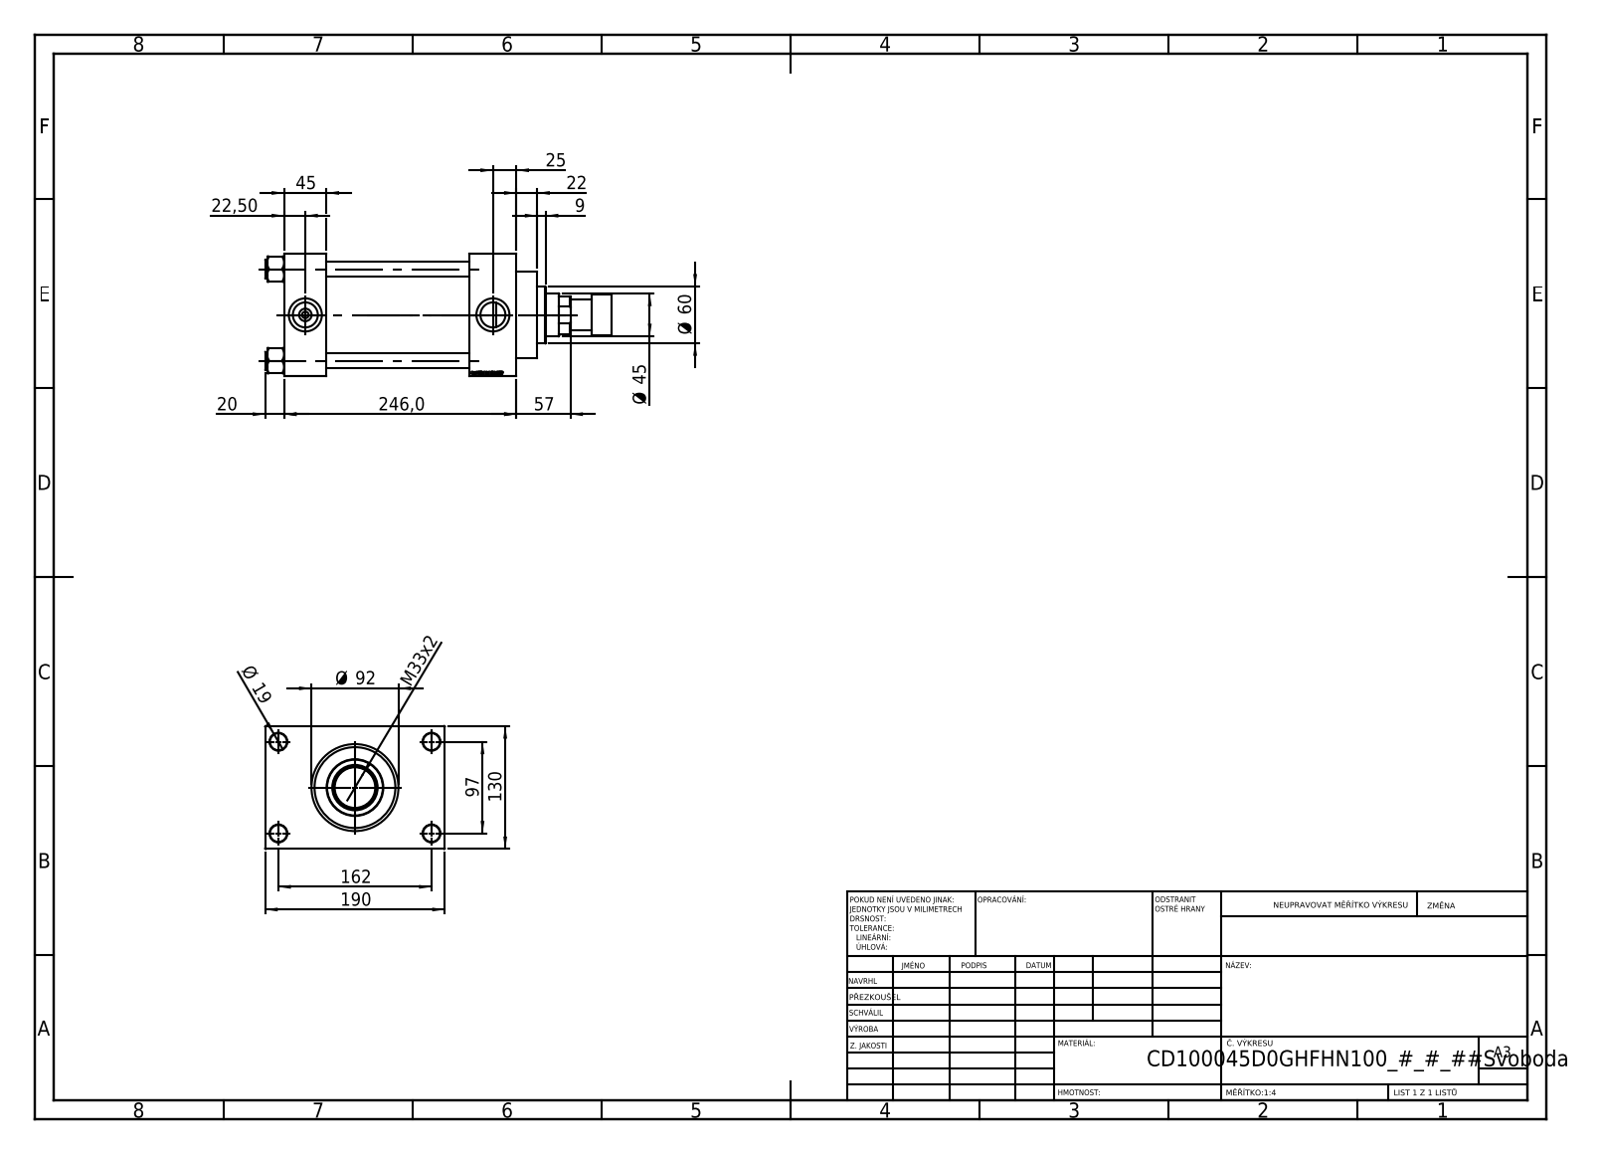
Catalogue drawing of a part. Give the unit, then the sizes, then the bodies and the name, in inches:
Units: inches
Overall size (bounding box): 14.449 × 7.48 × 5.118
Round holes (diameter × count): ⌀0.63 ×4, ⌀0.709 ×4, ⌀0.276 ×2, ⌀1.041 ×2, ⌀1.378 ×2, ⌀1.24 ×1, ⌀1.772 ×1, ⌀1.89 ×1, ⌀2.992 ×1, ⌀3.366 ×1, ⌀3.937 ×1
Round bosses / shafts (diameter × count): ⌀0.748 ×4, ⌀4.173 ×1, ⌀3.622 ×1, ⌀2.362 ×1, ⌀1.732 ×1, ⌀1.299 ×1
Main face-to-face distances: 5.118, 5.945, 1.772, 7.717, 9.685, 7.913, 1.969, 1.181, 6.299, 3.78
Hole centre spacings: 1.281, 2.698, 3.717, 3.815, 4.026, 5.096, 6.367, 3.819
Volume: 177.7 in³ · Surface area: 685.8 in²
Bodies: 12 solids, 1164 faces (548 planar, 92 cylindrical, 524 other)
Part name (STEP PRODUCT): V215CD_D_Body; V215CD_VCP_D; V215CD_NUT_M5_D; V215CD_D_TYCINKA (+2 more)
STEP written by: SolidWorks 2019 (CONFIG_CONTROL_DESIGN)
